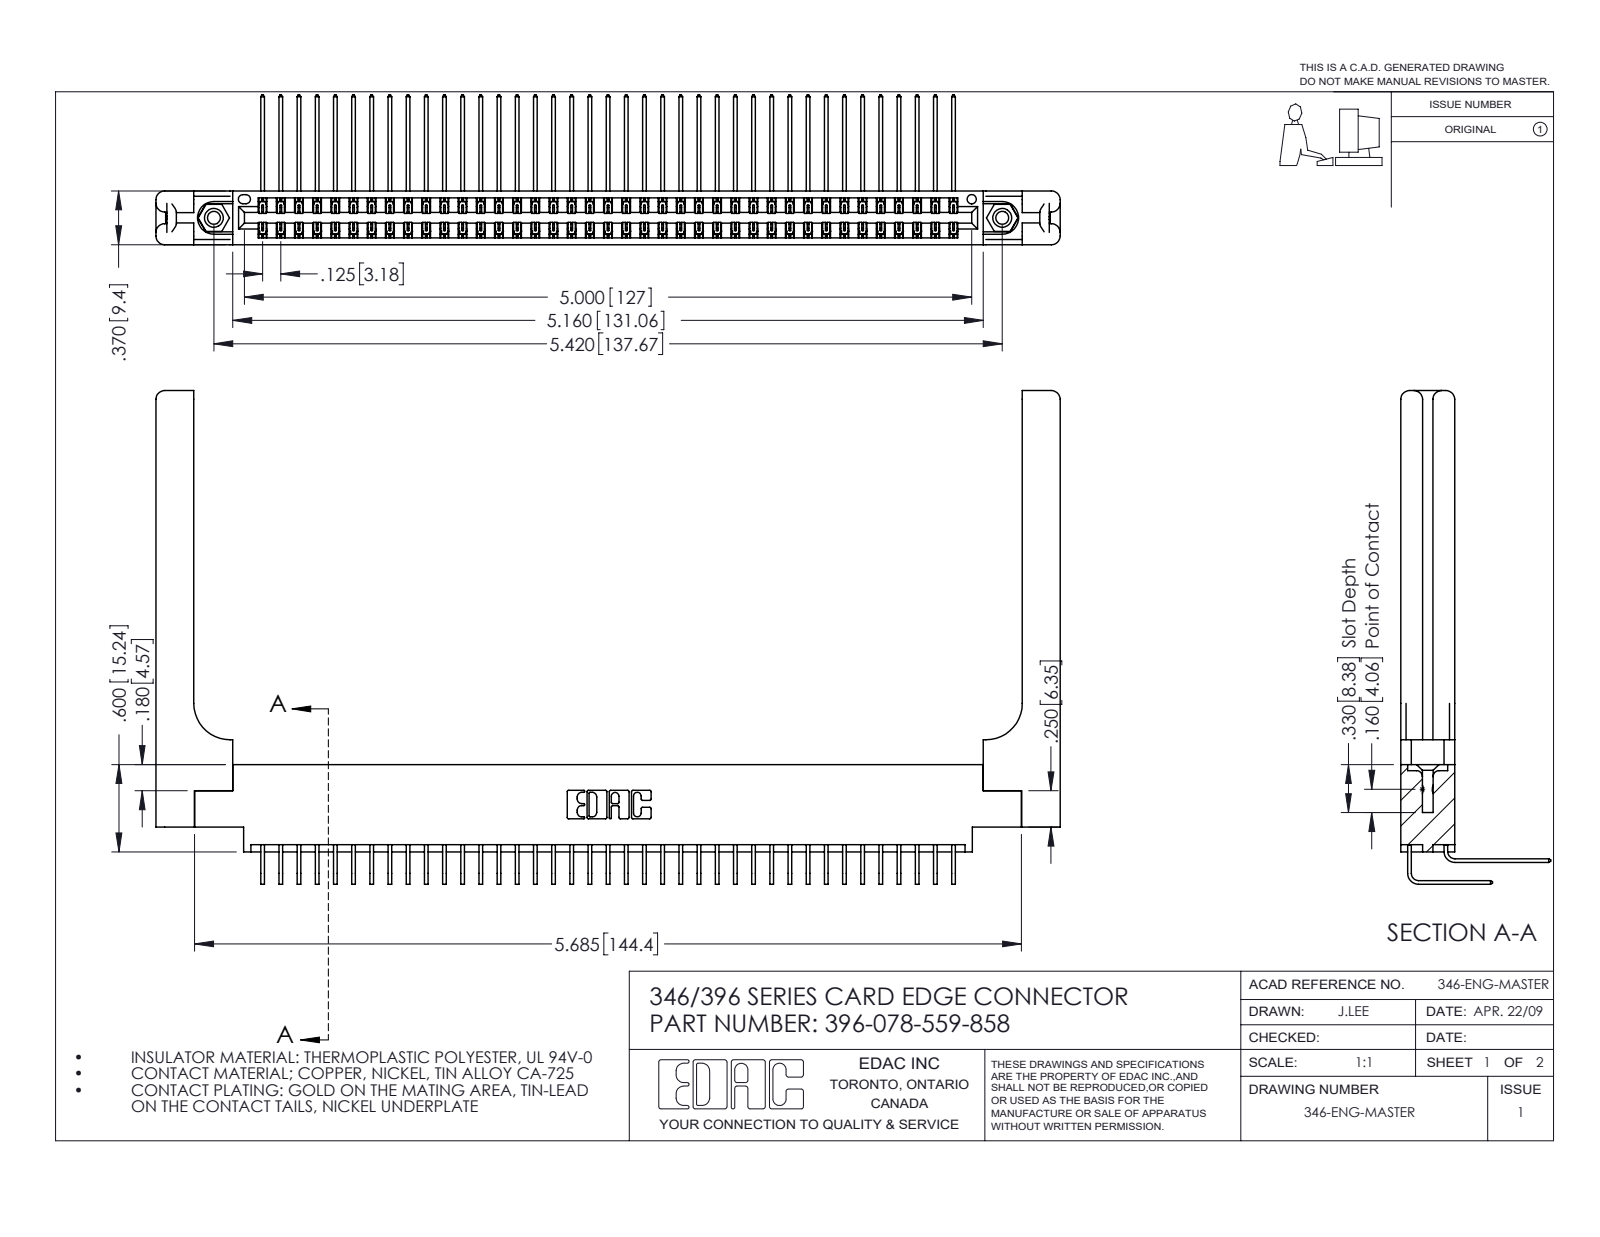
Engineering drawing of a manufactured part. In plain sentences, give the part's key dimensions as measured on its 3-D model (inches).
The part is named "345-292-001_558 559 Tail - 1; 396-078-559-858; 346-220-058_345-220-058; 346 Part_0.170 Offset - 0.156 Dia-TH (+2 more)". Its 3-D file was written by "SolidWorks 2016 (CONFIG_CONTROL_DESIGN)". It is 83 solids with 4594 faces: 3114 planar, 1420 cylindrical and 60 other. Overall it measures 6.216 by 3.393 by 1.03 inches. Its volume is 1.413 cubic inches and its surface area 44.64 square inches. Round holes: 2 of diameter 0.089, 2 of diameter 0.125, 2 of diameter 0.156, 1 of diameter 0.064. Round bosses or shafts: 2 of diameter 0.155. Partial cylindrical surfaces (rounded edges, fillets, slot ends): 117 of radius 0.006, 22 of radius 0.01, 16 of radius 0.06, 6 of radius 0.007, 6 of radius 0.031, 3 of radius 0.026, 2 of radius 0.014, 2 of radius 0.022. The main face-to-face distances are 0.37, 0.048, 0.322, 0.072, 0.025, 0.148, 0.15, 0.25, 0.298, 0.275. The hole center spacings are 0.246, 5.211, 5.42.
